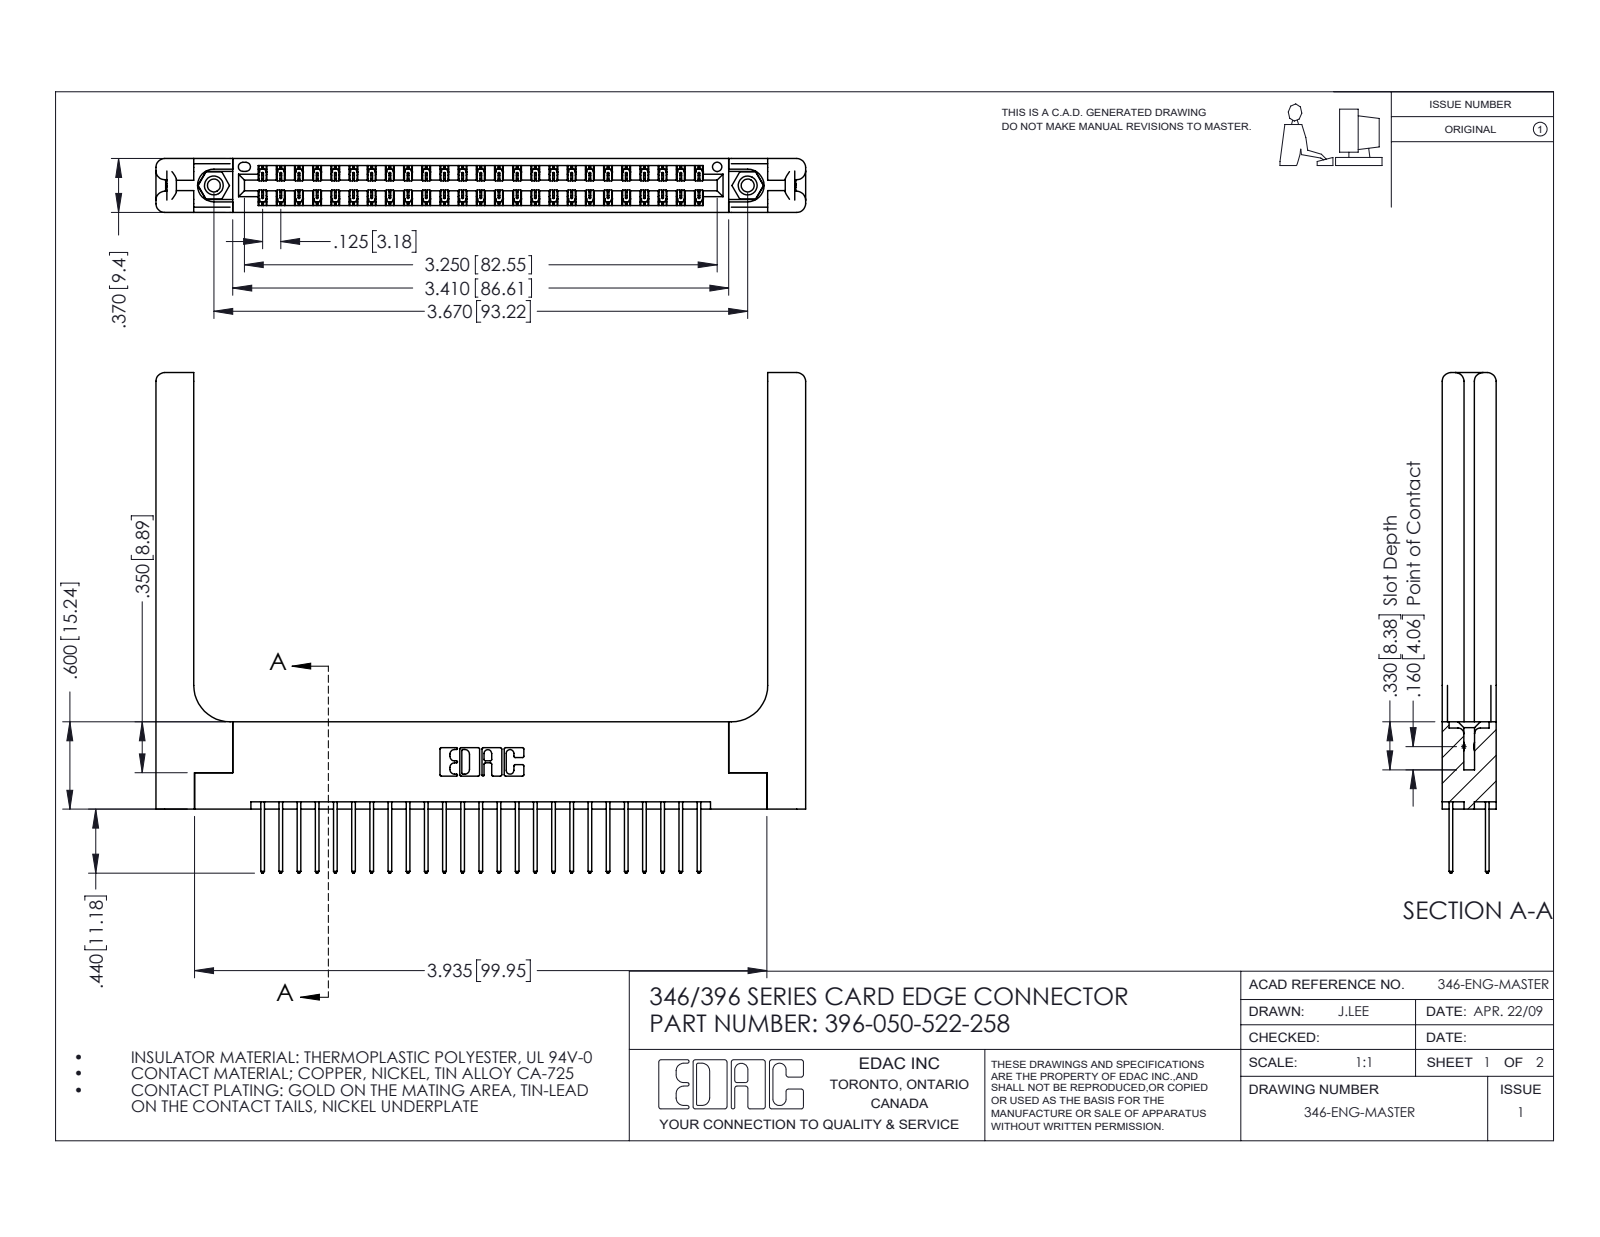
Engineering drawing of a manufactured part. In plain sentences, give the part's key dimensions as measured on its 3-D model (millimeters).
The part is named "345-250-001_345-250-001-102; 345-292-001_345-293-122; 346-220-058_345-220-058; 396-050-522-258 (+1 more)". Its 3-D file was written by "SolidWorks 2016 (CONFIG_CONTROL_DESIGN)". It is 55 solids with 2978 faces: 1974 planar, 944 cylindrical and 60 other. Overall it measures 113.4 by 87.4 by 9.4 millimeters. Its volume is 18 550 cubic millimeters and its surface area 20 500 square millimeters. Round holes: 2 of diameter 2.3, 2 of diameter 3.2, 2 of diameter 4, 1 of diameter 1.6. Round bosses or shafts: 2 of diameter 3.9. Partial cylindrical surfaces (rounded edges, fillets, slot ends): 75 of radius 0.2, 50 of radius 0.3, 22 of radius 0.3, 16 of radius 1.5, 6 of radius 0.2, 6 of radius 0.8, 3 of radius 0.7, 2 of radius 0.4. The main face-to-face distances are 9.4, 1.8, 1.2, 8.2, 6.4, 3.8, 3.8, 0.6, 7.6, 7. The hole center spacings are 6.2, 87.9, 93.2.
